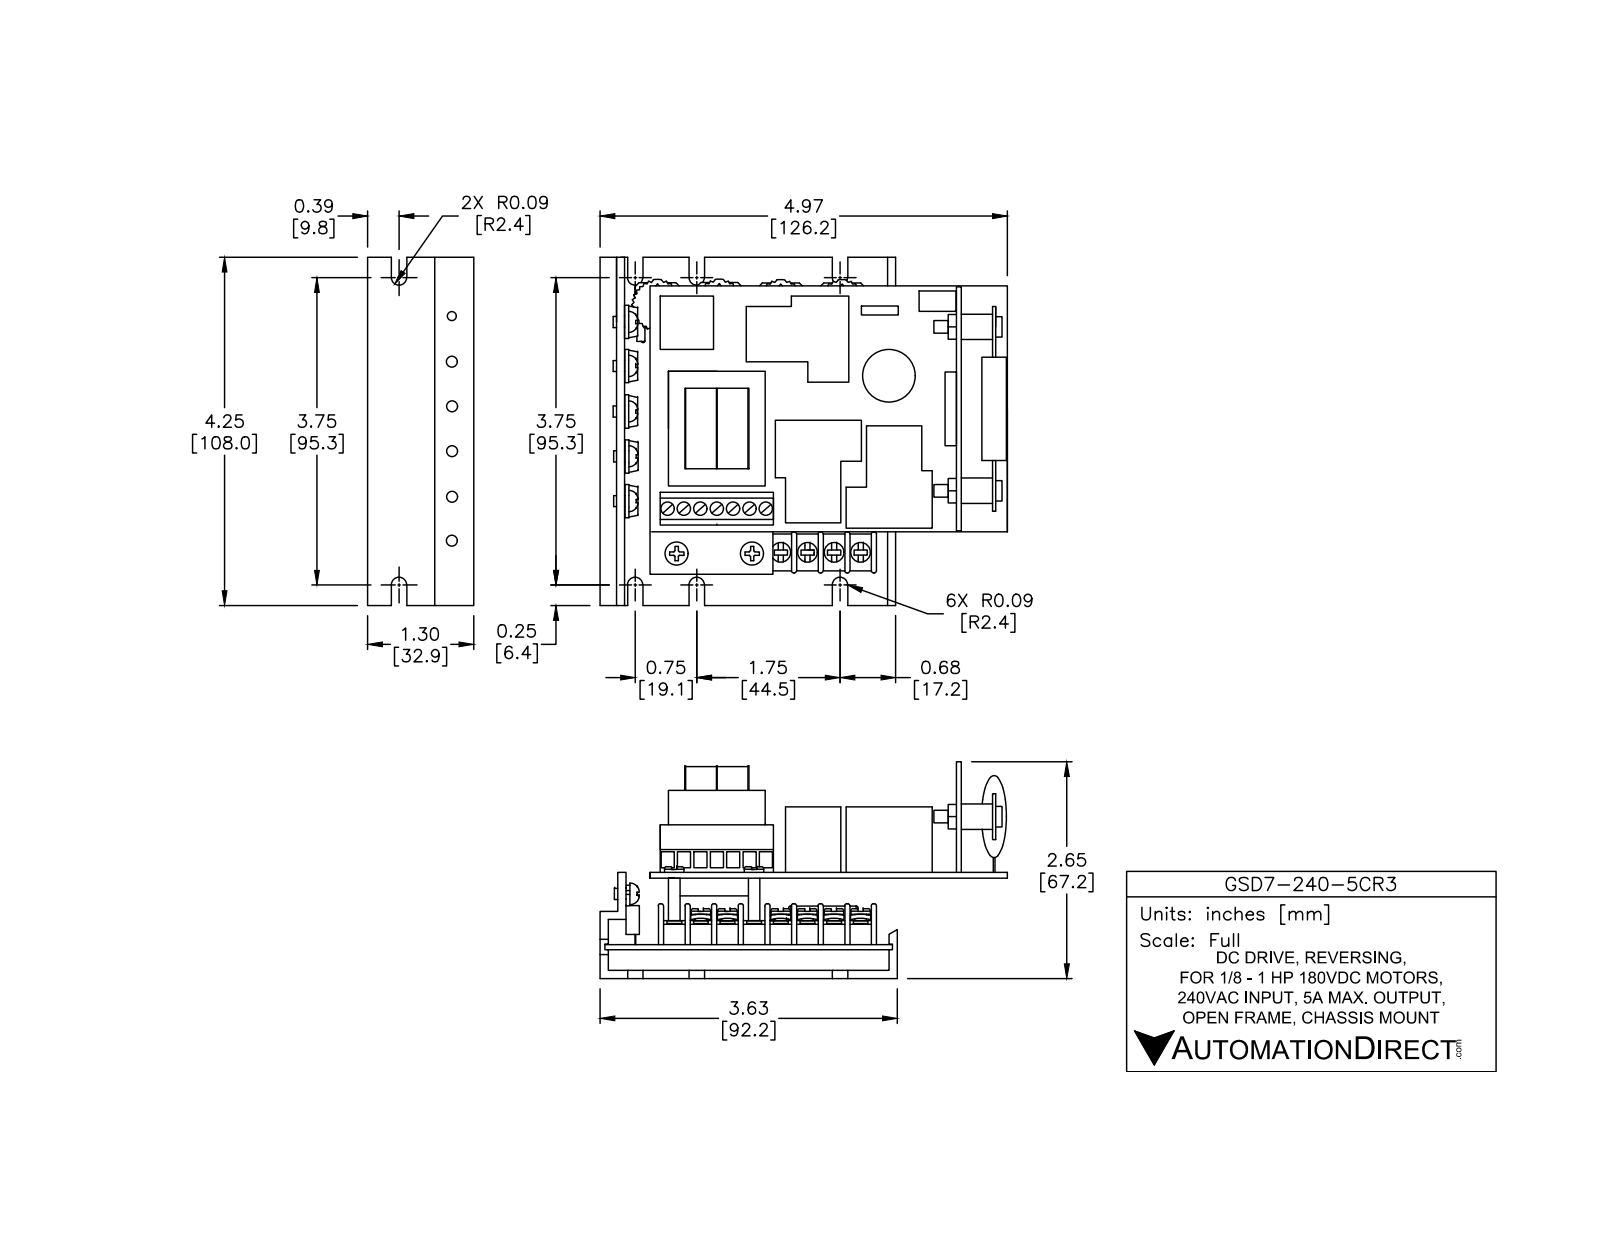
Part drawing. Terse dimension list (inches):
name: 130 Base Model Assembly; C6; DIOA500-120x240-40-RND; Standoff (+8 more)
written by: SolidWorks 2014 (AUTOMOTIVE_DESIGN)
unit: in
bodies: 99 solids, 5316 faces (2781 planar, 1893 cylindrical, 642 other)
size: 5.227 × 4.25 × 2.527
volume: 11.08 in³; area: 213.3 in²
holes: 90× ⌀0.033, 19× ⌀0.043, 16× ⌀0.035, 12× ⌀0.046, 9× ⌀0.07, 8× ⌀0.035, 7× ⌀0.09, 7× ⌀0.147, 6× ⌀0.04, 6× ⌀0.11, 5× ⌀0.144, 4× ⌀0.111
bosses: 43× ⌀0.025, 30× ⌀0.024, 22× ⌀0.025, 20× ⌀0.107, 19× ⌀0.081, 19× ⌀0.08, 16× ⌀0.03, 12× ⌀0.019
rounds: 23× R0.005, 12× R0.02, 12× R0.062, 11× R0.04, 10× R0.024, 8× R0.075, 8× R0.094, 6× R0.05
face distances: 0.1, 0.065, 1.127, 1.227, 0.25, 0.312, 0.75, 1.062, 1.162, 0.815
hole spacings: 0.2, 0.55, 0.1, 0.4, 0.461, 0.751, 0.636, 0.8
